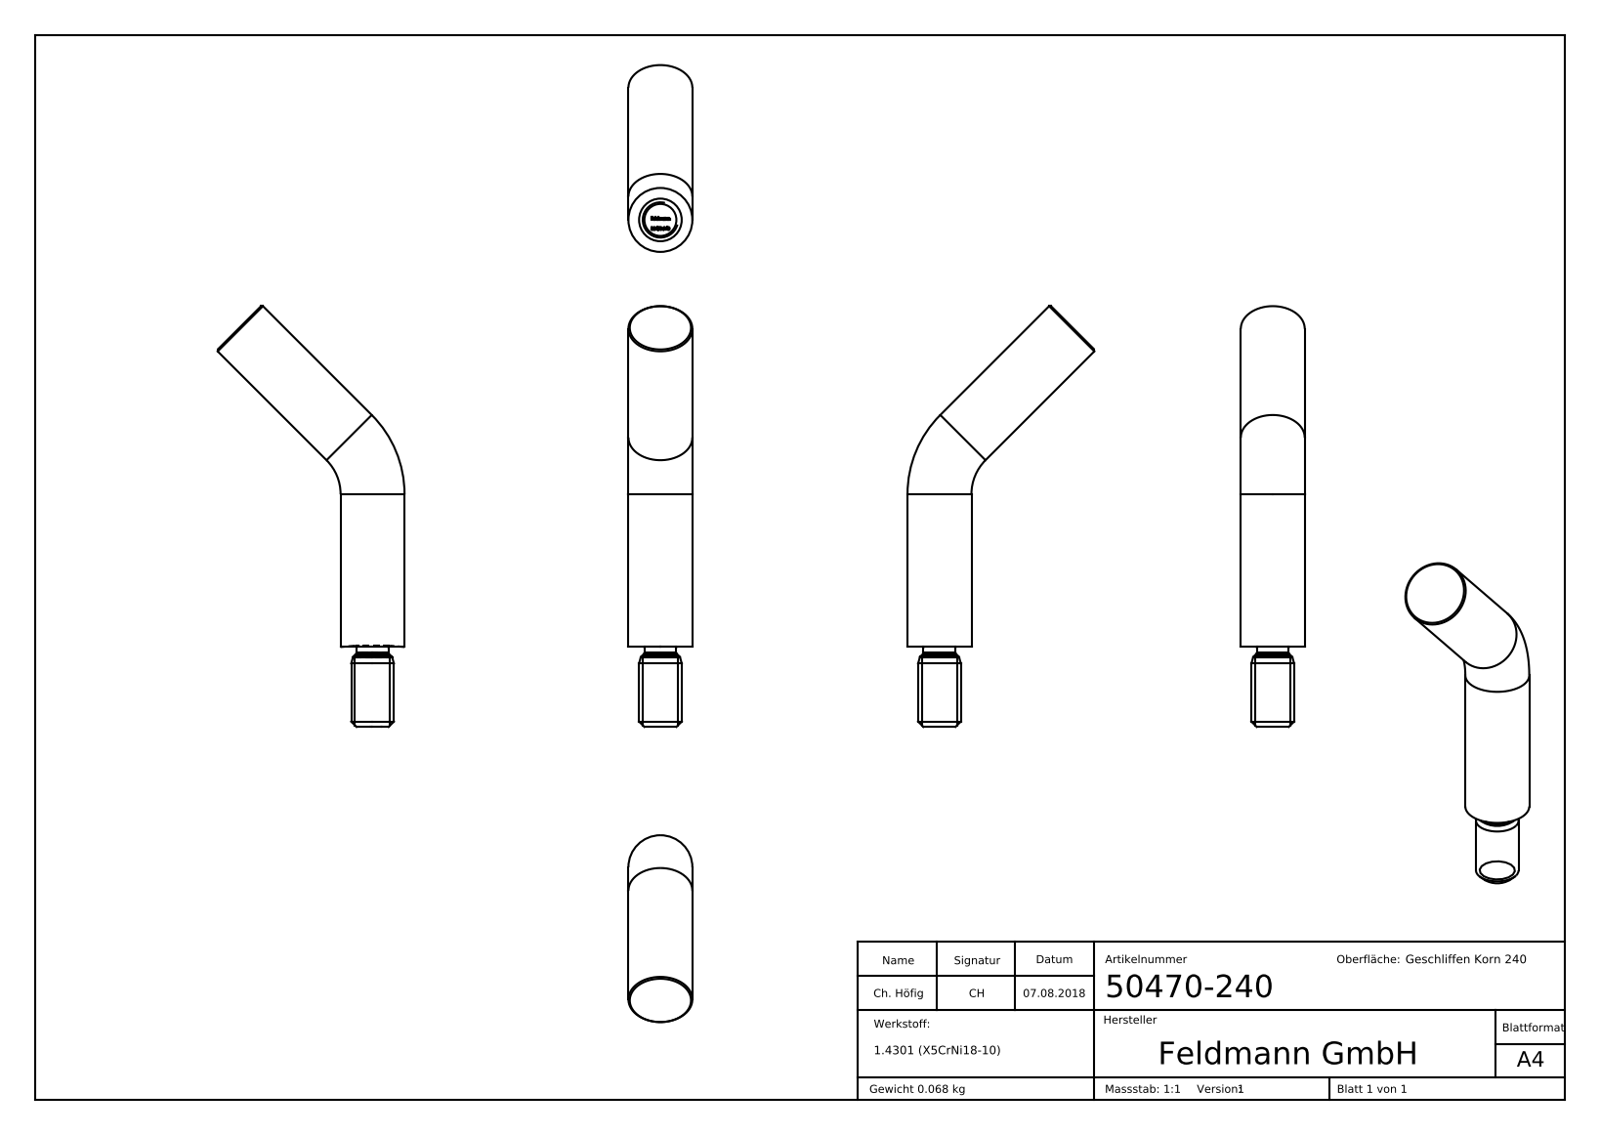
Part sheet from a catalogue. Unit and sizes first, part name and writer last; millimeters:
Units: millimetres
Overall size (bounding box): 78.98 × 35.07 × 12
Round bosses / shafts (diameter × count): ⌀12 ×2, ⌀8 ×1, ⌀6 ×1
Main face-to-face distances: 1.88, 1.19, 1.35, 0.53, 1.94, 1.83, 2.12, 0.66, 1.46, 0.41
Volume: 8 564 mm³ · Surface area: 3 230 mm²
Bodies: 1 solid, 246 faces (129 planar, 8 cylindrical, 109 other)
Part name (STEP PRODUCT): 50470-240
STEP written by: SolidWorks 2015 (CONFIG_CONTROL_DESIGN)
